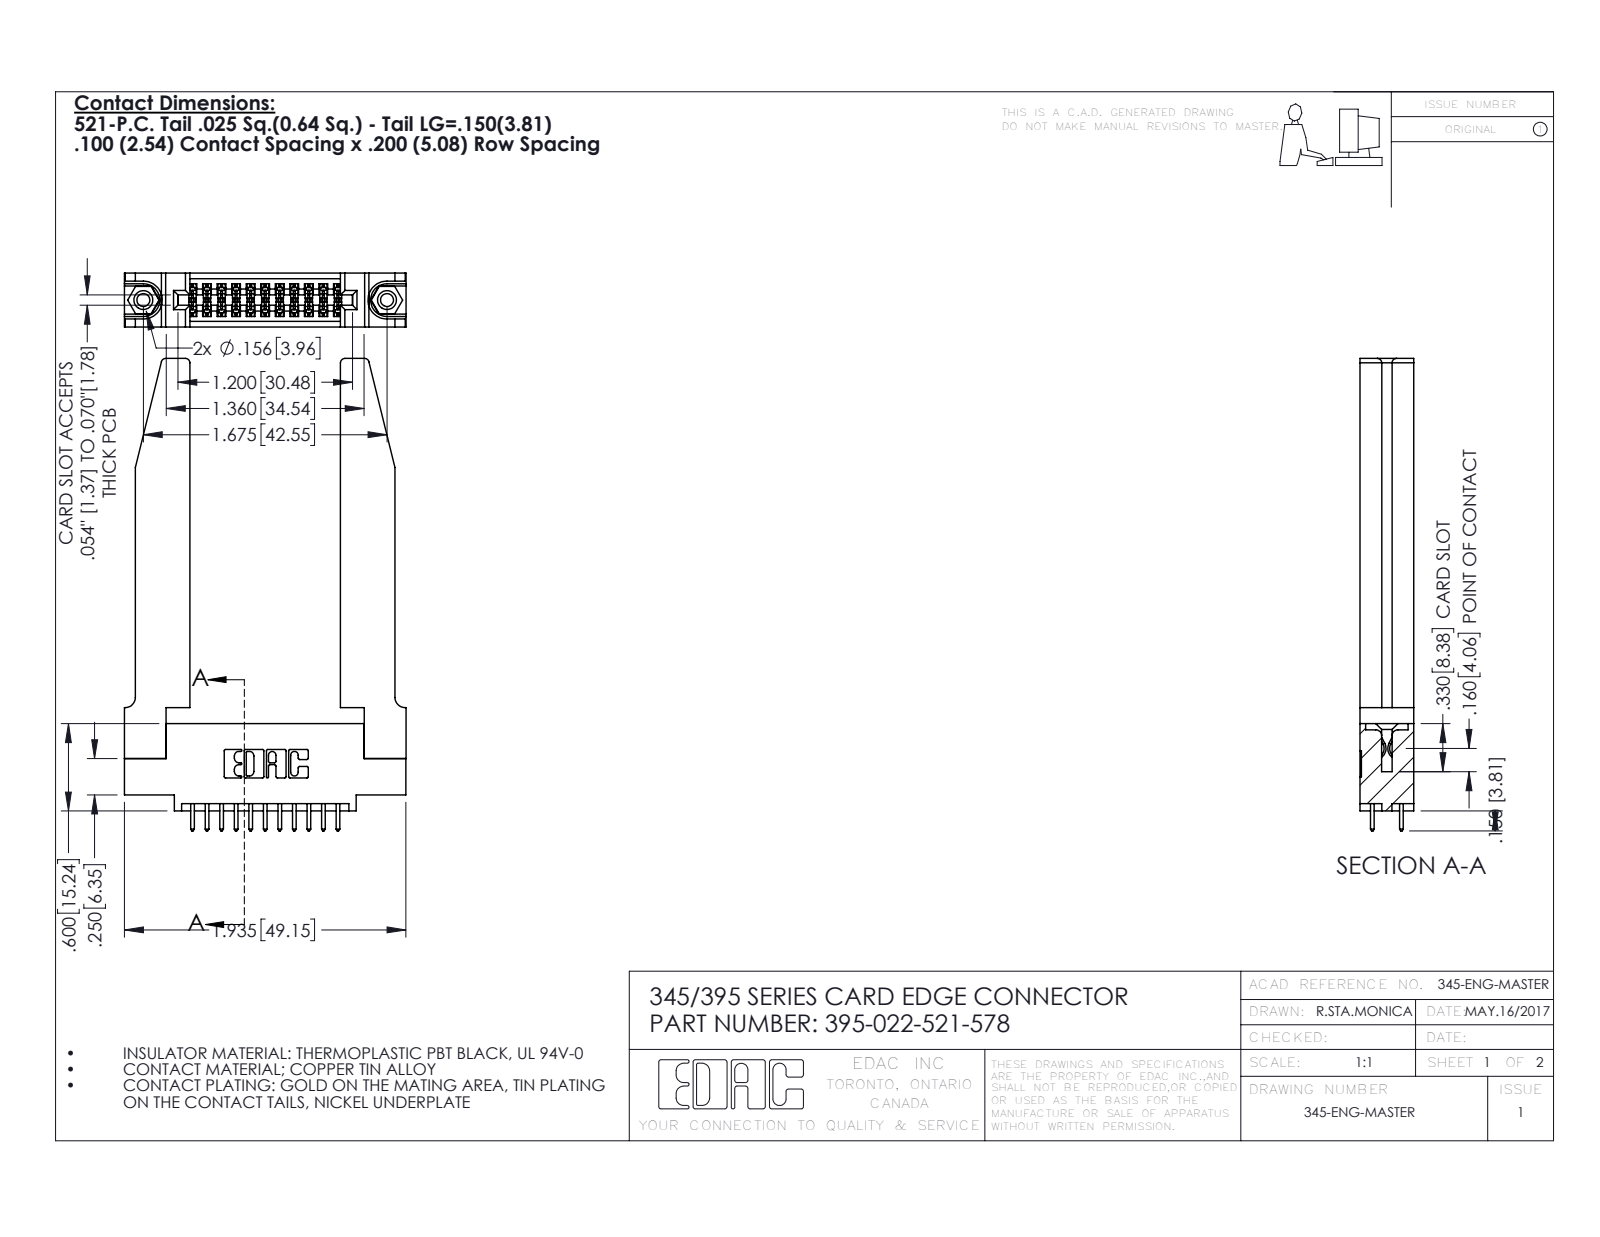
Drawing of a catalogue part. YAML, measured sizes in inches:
part_name: "395-022-521-578; 345-292-001_345-293-121; 345-220-078_345-220-078; 345 Part_0.110 Offset - 0.156 Dia-TH (+1 more)"
step_written_by: "SolidWorks 2016 (CONFIG_CONTROL_DESIGN)"
units: inches
bodies: {solids: 27, faces: 1464, planar: 952, cylindrical: 460, other: 52}
overall_size: [3.247, 1.936, 0.37]
volume: 0.743
surface_area: 19.82
round_holes:
  - {diameter: 0.089, count: 2}
  - {diameter: 0.125, count: 2}
  - {diameter: 0.156, count: 2}
  - {diameter: 0.064, count: 1}
round_bosses_or_shafts:
  - {diameter: 0.155, count: 2}
partial_cylinders:
  - {radius: 0.006, count: 33}
  - {radius: 0.01, count: 22}
  - {radius: 0.01, count: 22}
  - {radius: 0.03, count: 8}
  - {radius: 0.007, count: 6}
  - {radius: 0.031, count: 6}
  - {radius: 0.026, count: 3}
  - {radius: 0.014, count: 2}
face_to_face_distances: [0.37, 0.072, 0.298, 0.148, 0.15, 0.22, 0.077, 1.035, 0.2, 0.098]
hole_center_spacings: [0.27, 1.443, 1.675]
